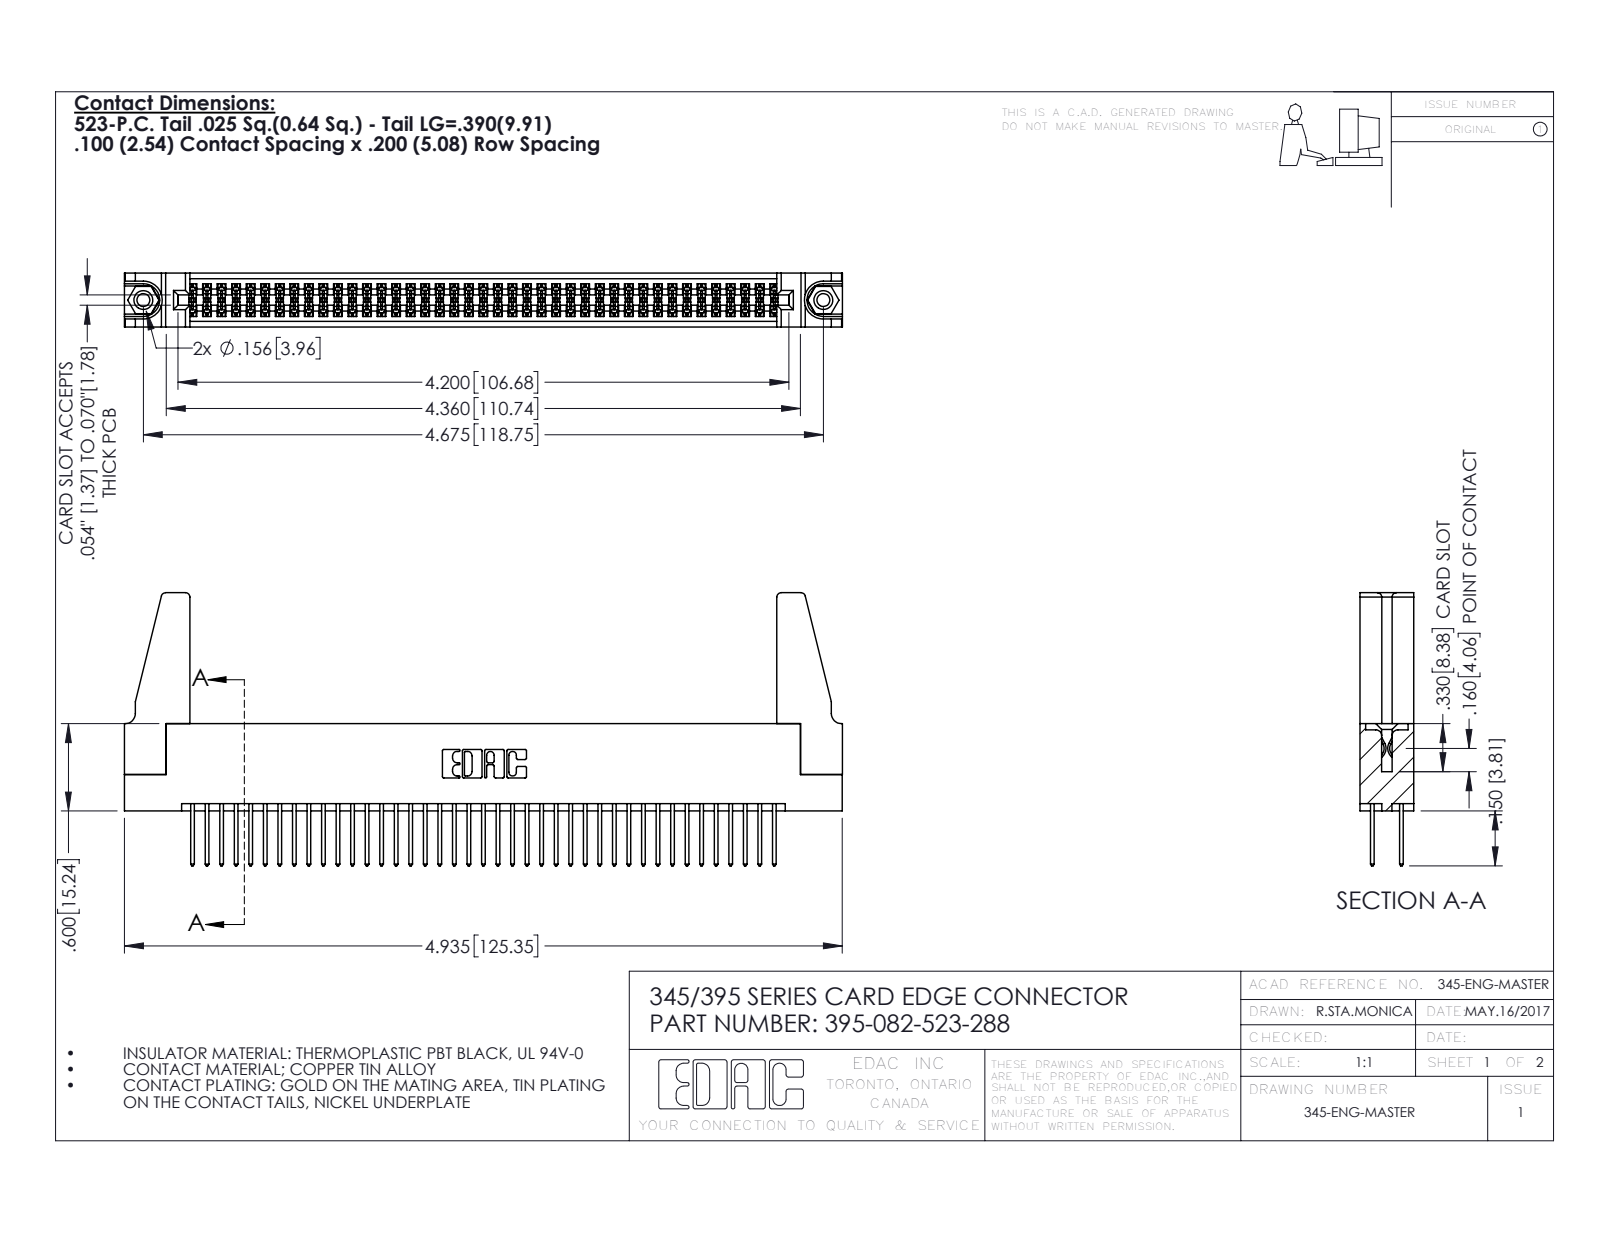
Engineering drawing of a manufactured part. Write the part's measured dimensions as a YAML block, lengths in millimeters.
part_name: "345 Part_Flush Mounting Lugs - 0.156 Dia-TH; 345-250-001_345-250-001-102; 345-220-078_345-220-088; 395-082-523-288 (+1 more)"
step_written_by: "SolidWorks 2016 (CONFIG_CONTROL_DESIGN)"
units: millimeters
bodies: {solids: 87, faces: 4350, planar: 2858, cylindrical: 1476, other: 16}
overall_size: [125.4, 47.7, 9.4]
volume: 15600
surface_area: 22100
round_holes:
  - {diameter: 2.3, count: 2}
  - {diameter: 3.2, count: 2}
  - {diameter: 4, count: 2}
  - {diameter: 1.6, count: 1}
round_bosses_or_shafts:
  - {diameter: 3.9, count: 2}
partial_cylinders:
  - {radius: 0.2, count: 123}
  - {radius: 0.3, count: 82}
  - {radius: 0.3, count: 22}
  - {radius: 0.8, count: 8}
  - {radius: 0.2, count: 6}
  - {radius: 0.8, count: 6}
  - {radius: 0.7, count: 3}
  - {radius: 0.4, count: 2}
face_to_face_distances: [1.8, 7.6, 5.1, 9.4, 2.5, 6.9, 0.6, 5.7, 4.4, 3.8]
hole_center_spacings: [6.9, 112.8, 118.7]
